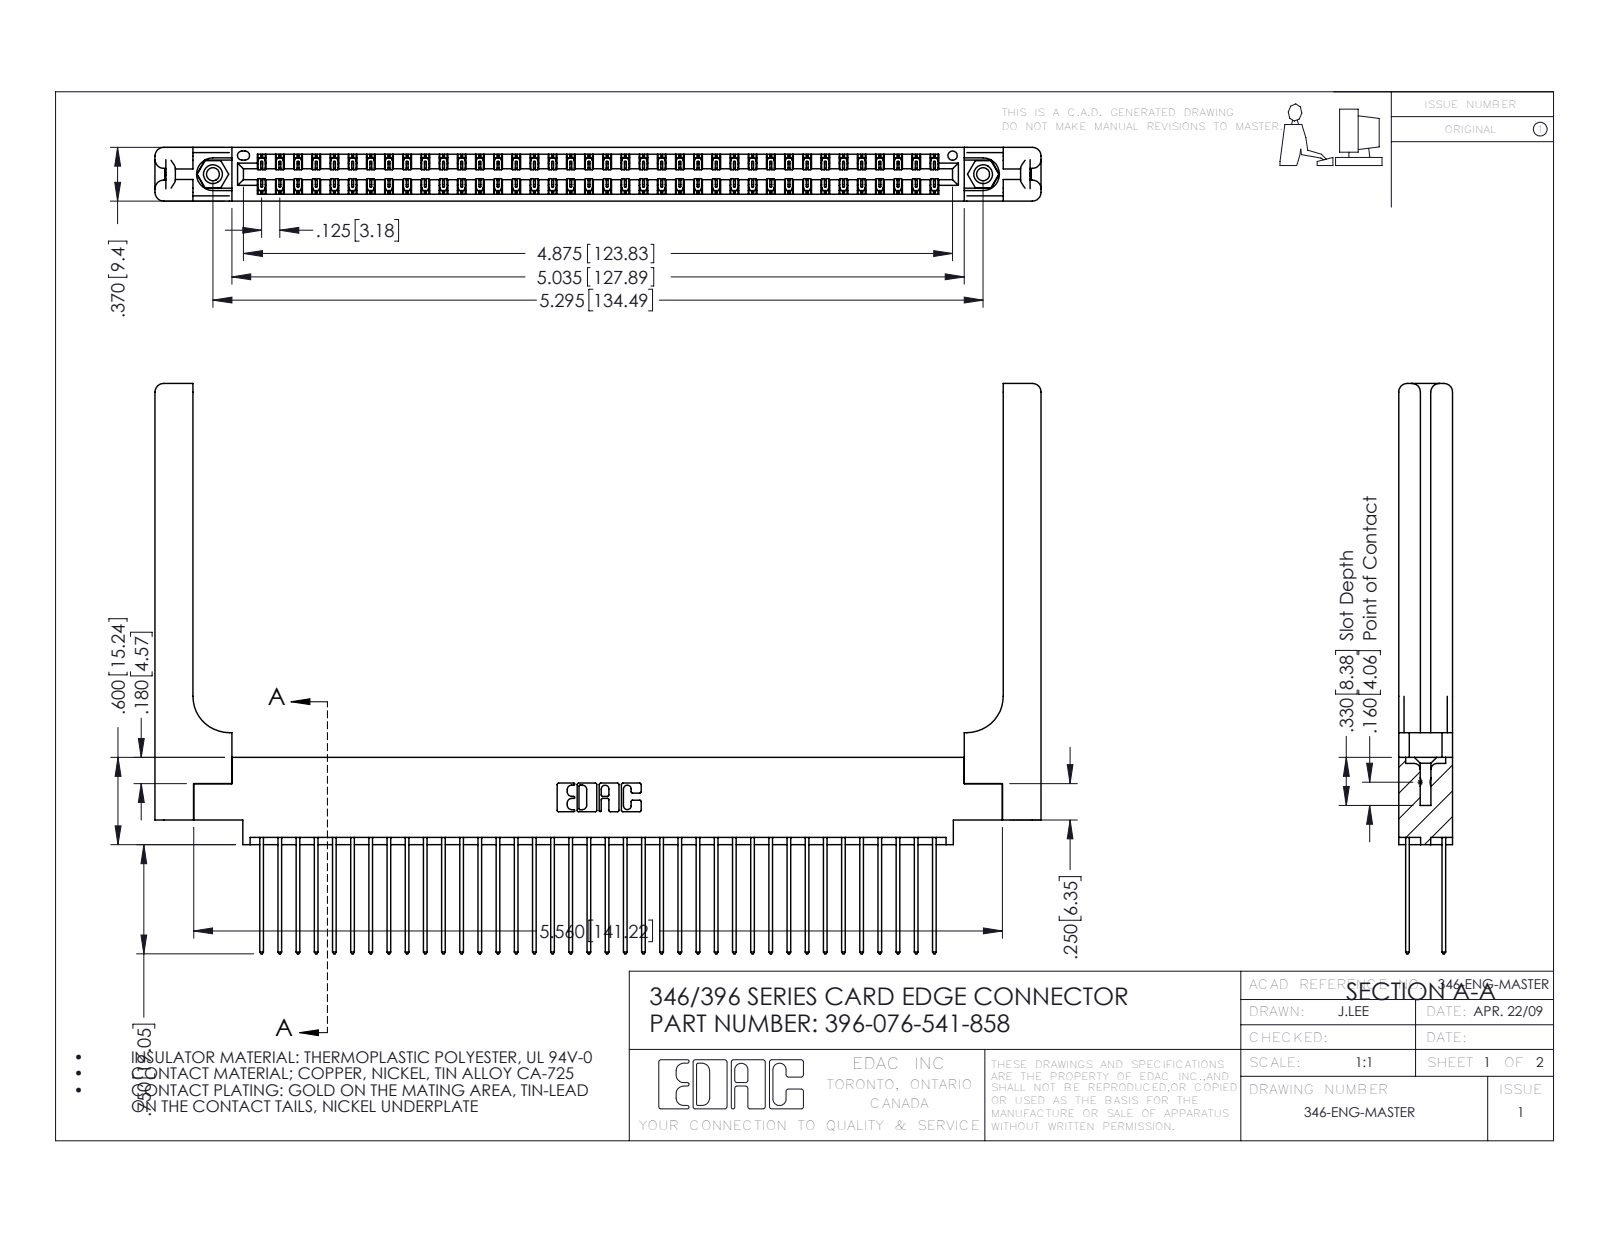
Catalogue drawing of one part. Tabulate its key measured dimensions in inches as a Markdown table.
| quantity | value |
| --- | --- |
| part name | 346-220-058_345-220-058; 396-076-541-858; 346 Part_0.170 Offset - 0.156 Dia-TH; 345-250-001_345-250-001-102 (+1 more) |
| STEP written by | SolidWorks 2016 (CONFIG_CONTROL_DESIGN) |
| units | inches |
| bodies | 81 solids, 4334 faces (2888 planar, 1386 cylindrical, 60 other) |
| overall size | 6.091 × 3.92 × 0.37 |
| volume | 1.393 in³ |
| surface area | 43.81 in² |
| round holes (diameter × count) | 0.089 × 2, 0.125 × 2, 0.156 × 2, 0.064 × 1 |
| round bosses / shafts (diameter × count) | 0.155 × 2 |
| partial cylindrical surfaces (radius × count) | 0.006 × 114, 0.01 × 76, 0.01 × 22, 0.06 × 16, 0.007 × 6, 0.031 × 6, 0.026 × 3, 0.014 × 2 |
| main face-to-face distances | 0.048, 0.322, 0.072, 0.37, 0.25, 0.025, 0.298, 0.148, 0.15, 0.275 |
| hole center spacings | 0.246, 5.086, 5.295 |
